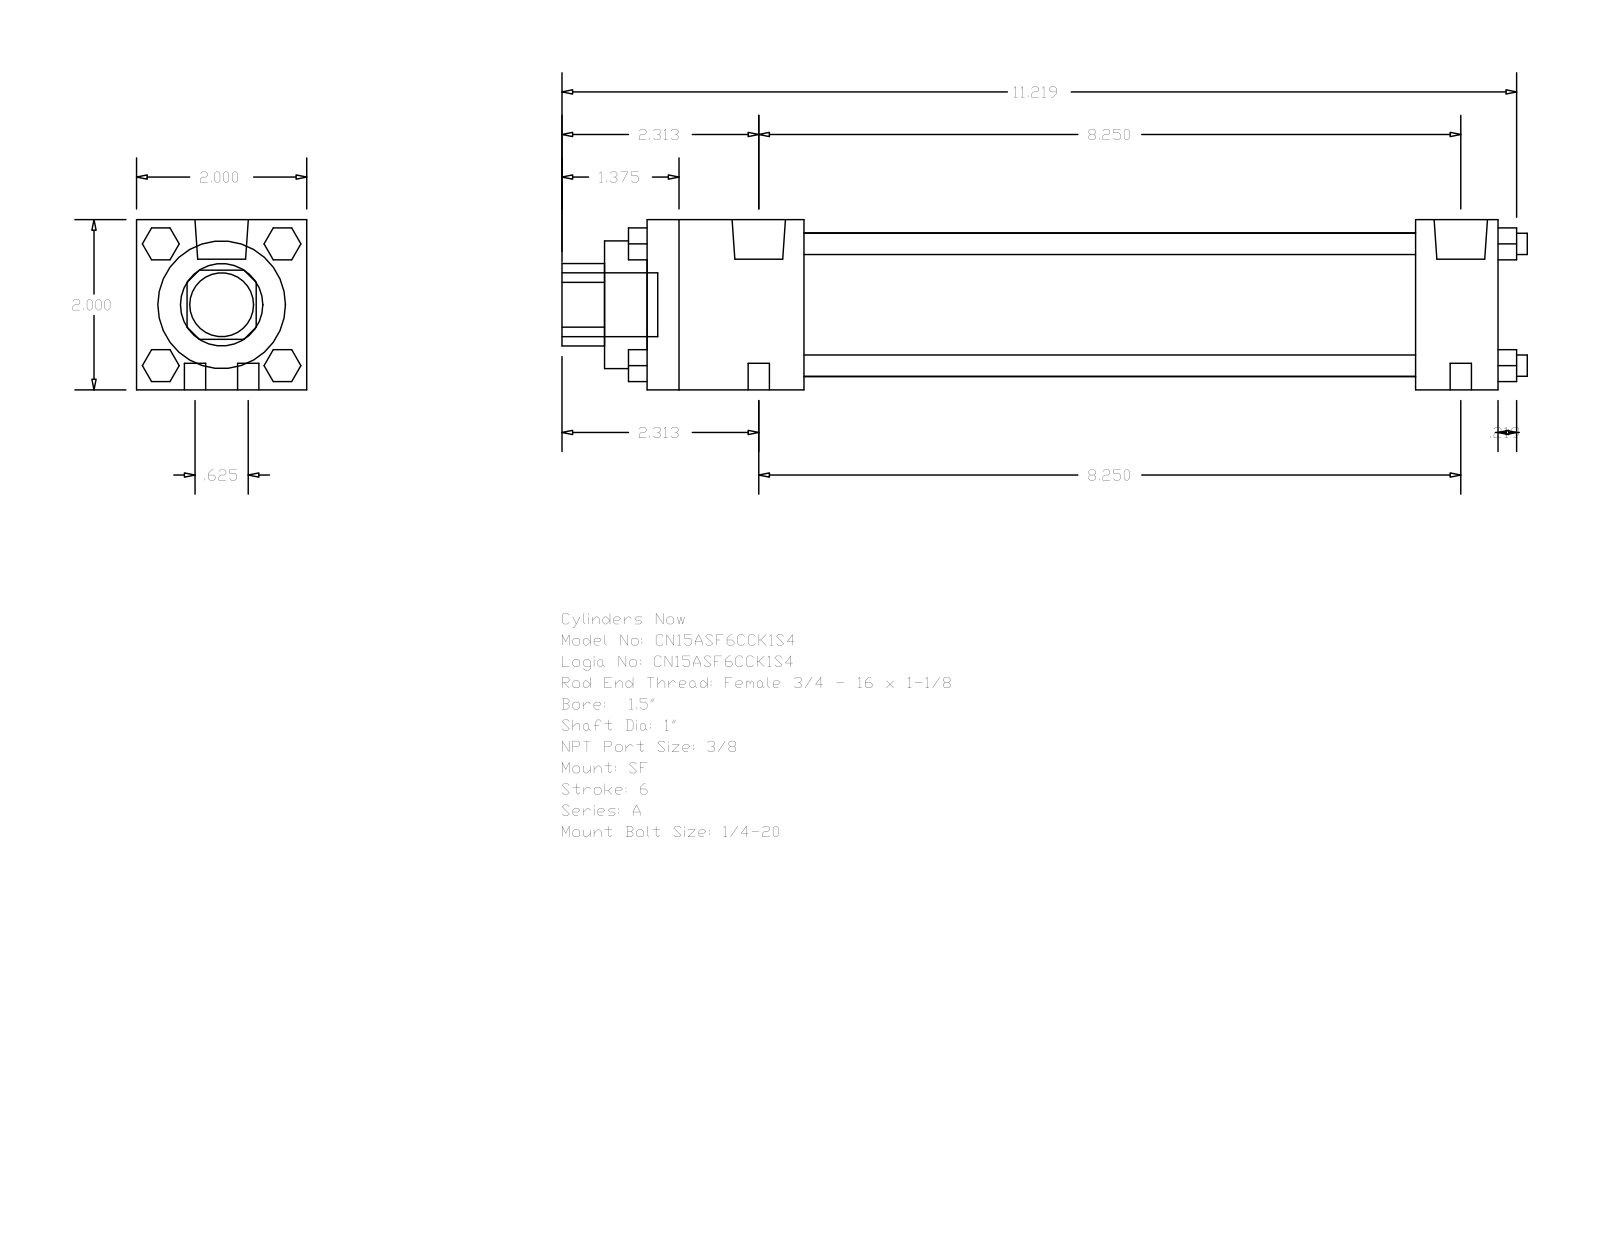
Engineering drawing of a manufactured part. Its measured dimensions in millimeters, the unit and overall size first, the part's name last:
Units: millimetres
Overall size (bounding box): 288.13 × 50.8 × 50.8
Round holes (diameter × count): ⌀25.4 ×1, ⌀38.1 ×1, ⌀42.93 ×1
Round bosses / shafts (diameter × count): ⌀6.35 ×8, ⌀15.93 ×2, ⌀5.56 ×2, ⌀19.05 ×1
Partial cylindrical surfaces — rounded edges, fillets, slot ends (radius × count): R12.29 ×1
Main face-to-face distances: 50.8, 254, 46.83, 229.39, 182.56, 207.17, 24.61, 12.7, 59.53, 242.09
Bodies: 0 solids, 124 faces (94 planar, 30 cylindrical, 0 other)
Part name (STEP PRODUCT): A_SF__0150_1
STEP written by: GSSL Pune (CONFIG_CONTROL_DESIGN)
